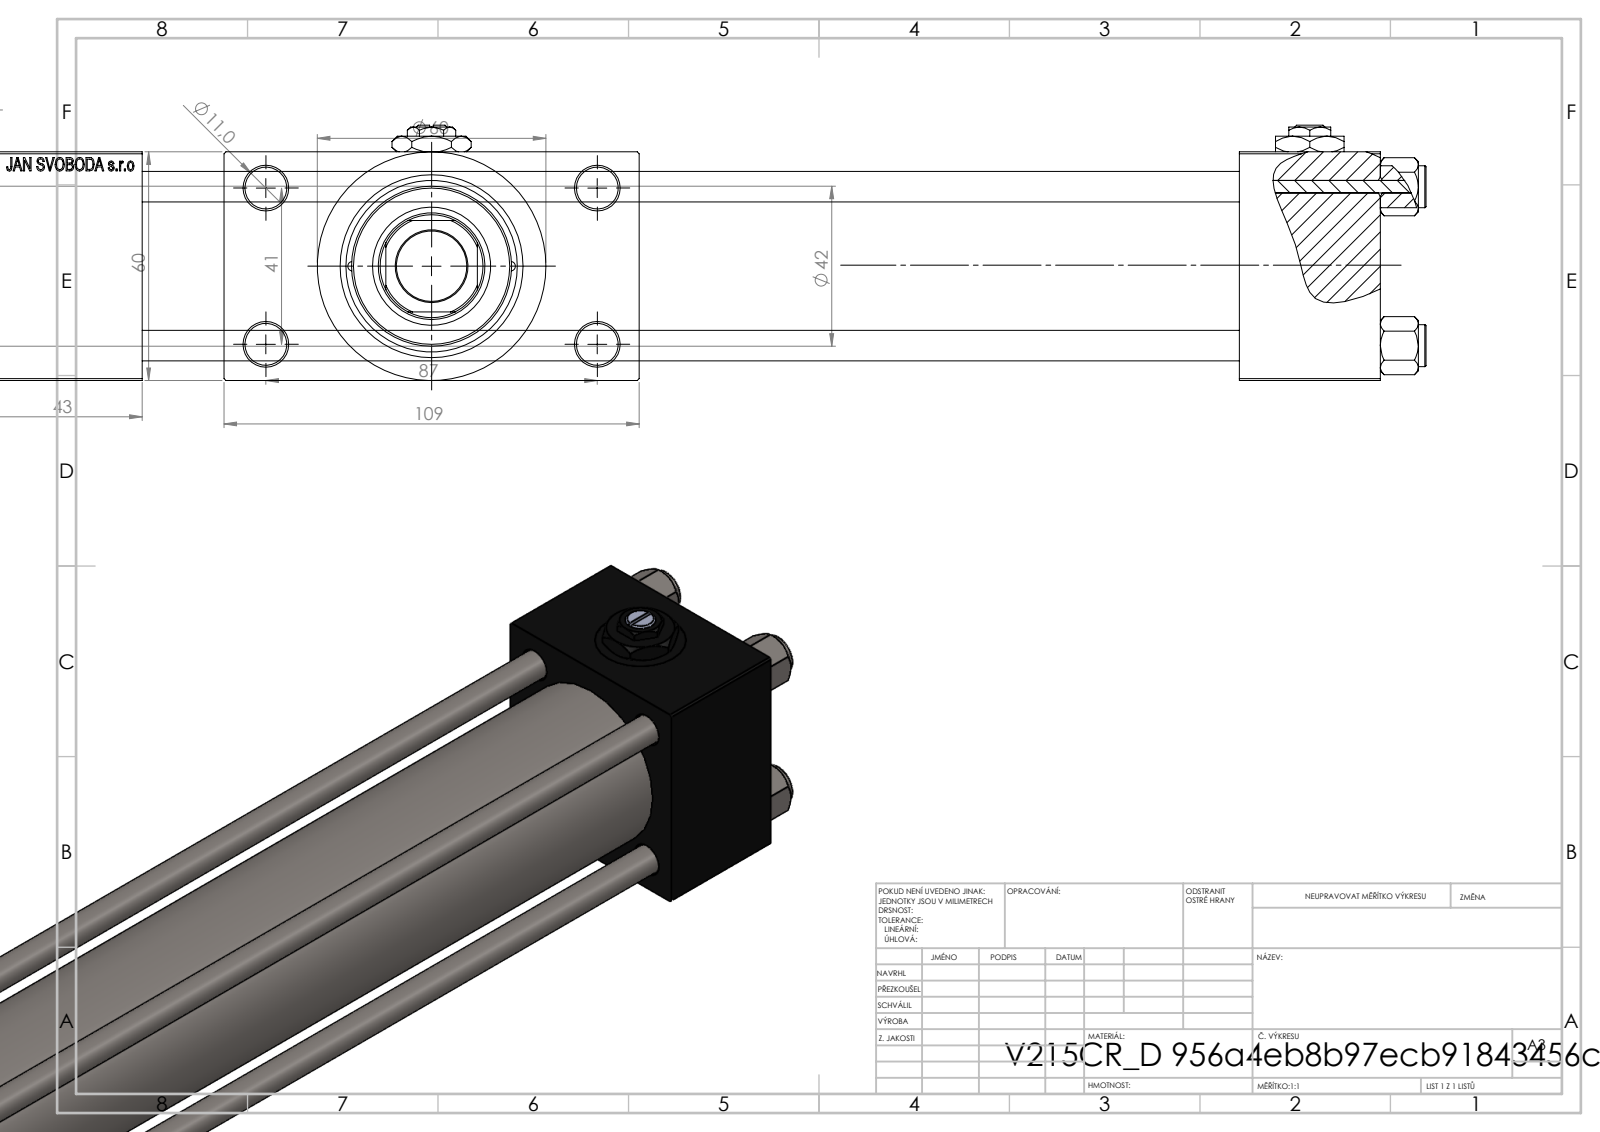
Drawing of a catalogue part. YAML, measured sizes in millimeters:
part_name: "V215CR_VCP_D; NUT_M5_D; V215CR_D_TYCINKA; V215CR_D_Body (+2 more)"
step_written_by: "SolidWorks 2019 (CONFIG_CONTROL_DESIGN)"
units: millimeters
bodies: {solids: 12, faces: 1167, planar: 526, cylindrical: 99, other: 542}
overall_size: [415, 109, 67]
volume: 807991
surface_area: 236304
round_holes:
  - {diameter: 8, count: 4}
  - {diameter: 11, count: 4}
  - {diameter: 7, count: 3}
  - {diameter: 16.66, count: 3}
  - {diameter: 24, count: 3}
  - {diameter: 2.5, count: 2}
  - {diameter: 18.5, count: 1}
  - {diameter: 28, count: 1}
  - {diameter: 31, count: 1}
  - {diameter: 40, count: 1}
  - {diameter: 45, count: 1}
round_bosses_or_shafts:
  - {diameter: 11, count: 4}
  - {diameter: 60, count: 1}
  - {diameter: 46, count: 1}
  - {diameter: 42, count: 1}
partial_cylinders:
  - {radius: 13.5, count: 1}
face_to_face_distances: [60, 24.5, 288, 84.5, 37, 325, 368, 331, 43, 109]
hole_center_spacings: [20.85, 22.65, 29.49, 30.62, 41.7, 46.53, 47.15, 48.09]
